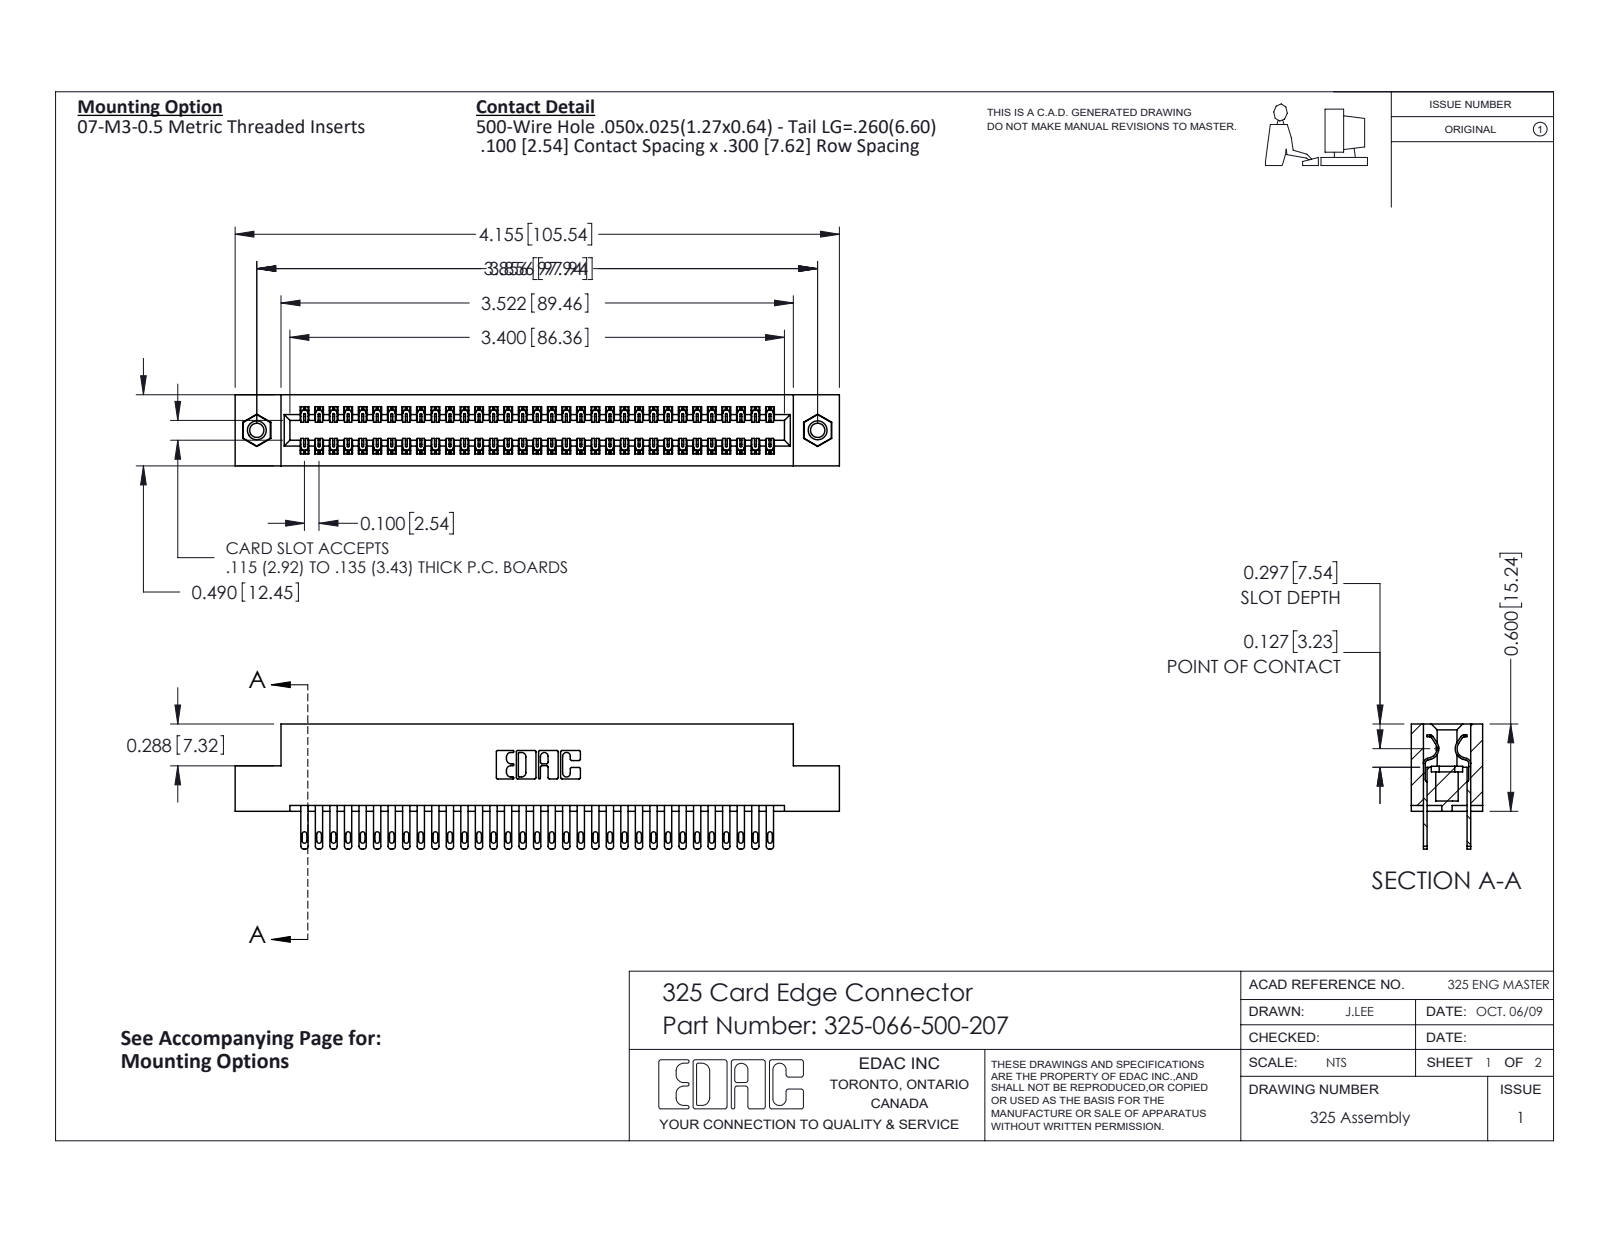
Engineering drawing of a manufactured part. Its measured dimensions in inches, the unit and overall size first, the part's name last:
Units: inches
Overall size (bounding box): 4.155 × 0.86 × 0.49
Round holes (diameter × count): ⌀0.098 ×2, ⌀0.125 ×2, ⌀0.16 ×2
Round bosses / shafts (diameter × count): ⌀0.155 ×2
Partial cylindrical surfaces — rounded edges, fillets, slot ends (radius × count): R0.006 ×99, R0.016 ×66, R0.02 ×66, R0.01 ×22, R0.007 ×6, R0.031 ×6, R0.026 ×3, R0.014 ×2
Main face-to-face distances: 0.083, 0.407, 0.3, 0.107, 0.383, 0.025, 0.49, 0.325, 0.275, 0.56
Hole centre spacings: 3.856
Volume: 0.838 in³ · Surface area: 26.54 in²
Bodies: 69 solids, 3342 faces (2082 planar, 1244 cylindrical, 16 other)
Part name (STEP PRODUCT): 325-292-001_325-293-100; 325 Part_TI; 325-066-500-207; 345-250-001_345-250-005-103
STEP written by: SolidWorks 2016 (CONFIG_CONTROL_DESIGN)
